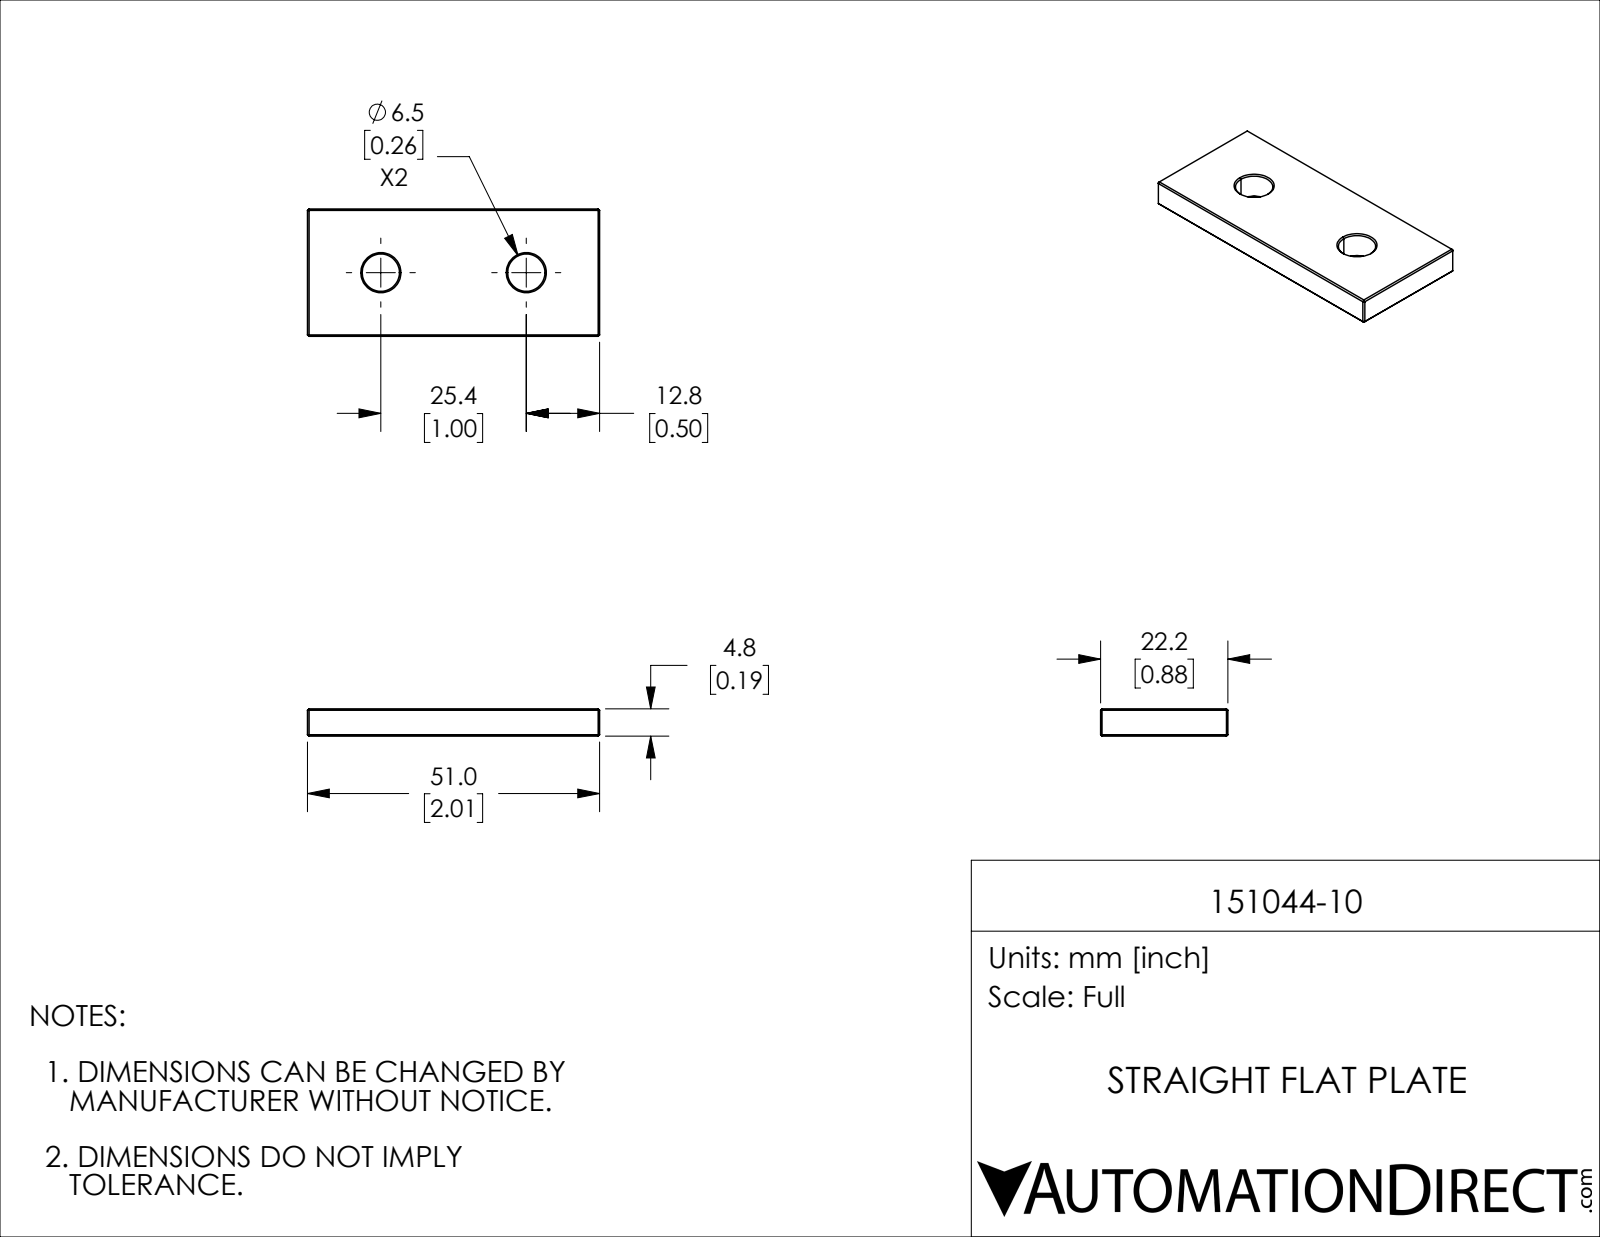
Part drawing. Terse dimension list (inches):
name: 151044-10
written by: SolidWorks 2024 (CONFIG_CONTROL_DESIGN)
unit: in
bodies: 1 solid, 38 faces (26 planar, 4 cylindrical, 8 other)
size: 2.008 × 0.875 × 0.187
volume: 0.309 in³; area: 4.602 in²
holes: 2× ⌀0.256
face distances: 0.187, 0.875, 2.008, 0.737, 1.538, 2.024, 1.749
hole spacings: 1
